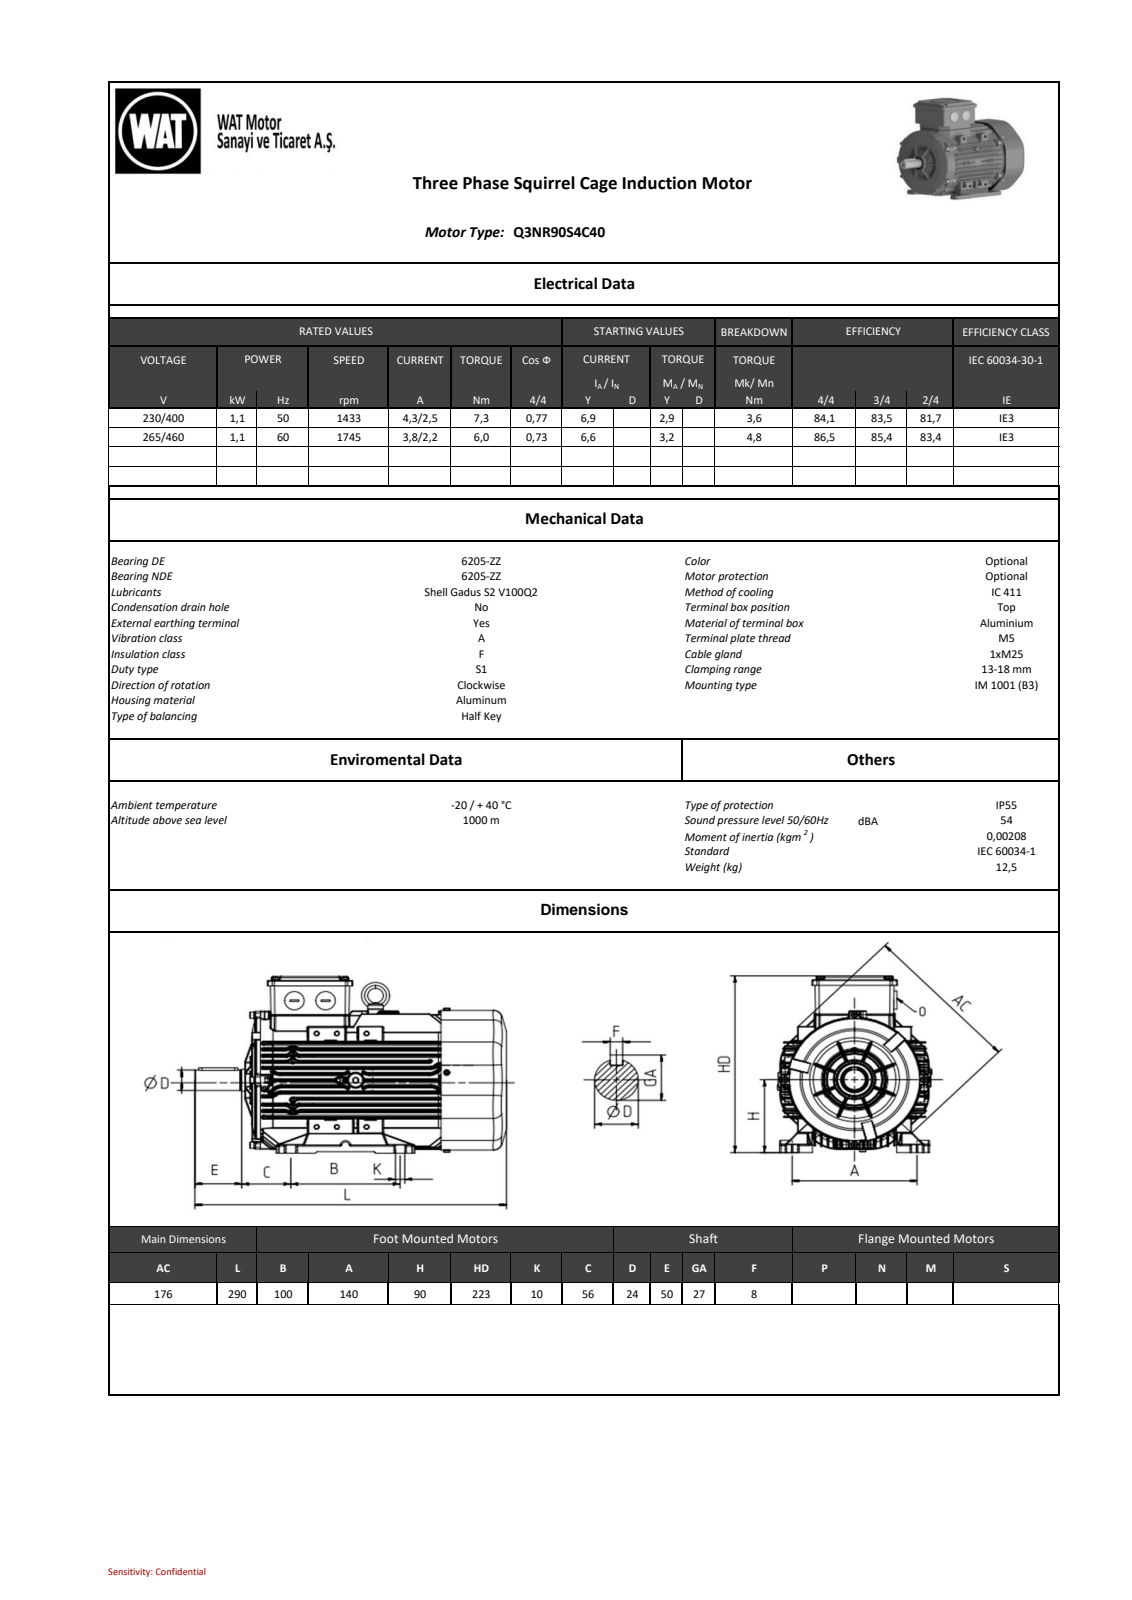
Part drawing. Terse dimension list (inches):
name: C901535CCA47uolb
written by: SIEMENS PLM Software NX 11.0 (AUTOMOTIVE_DESIGN)
unit: in
bodies: 0 solids, 15311 faces (3502 planar, 4422 cylindrical, 7387 other)
size: 11.417 × 8.268 × 7.087
holes: 6× ⌀0.165, 6× ⌀0.201, 6× ⌀0.354, 4× ⌀0.472, 2× ⌀0.079, 2× ⌀0.098, 2× ⌀0.118, 2× ⌀0.276, 2× ⌀0.92, 1× ⌀0.157, 1× ⌀0.315, 1× ⌀0.48
bosses: 12× ⌀0.197, 8× ⌀0.315, 8× ⌀0.157, 6× ⌀0.37, 6× ⌀0.362, 6× ⌀0.335, 3× ⌀0.984, 2× ⌀1.39
rounds: 1190× R0.02, 711× R0.039, 509× R0.031, 144× R0.008, 120× R0.012, 88× R0.079, 88× R0.157, 86× R0.059
face distances: 0.031, 0.217, 2.205, 0.217, 1.535, 1.102, 0.229, 5.039, 0.194, 0.079
hole spacings: 0.787, 3.189, 0.557, 0.557, 1.113, 3.659, 5.224, 0.567
